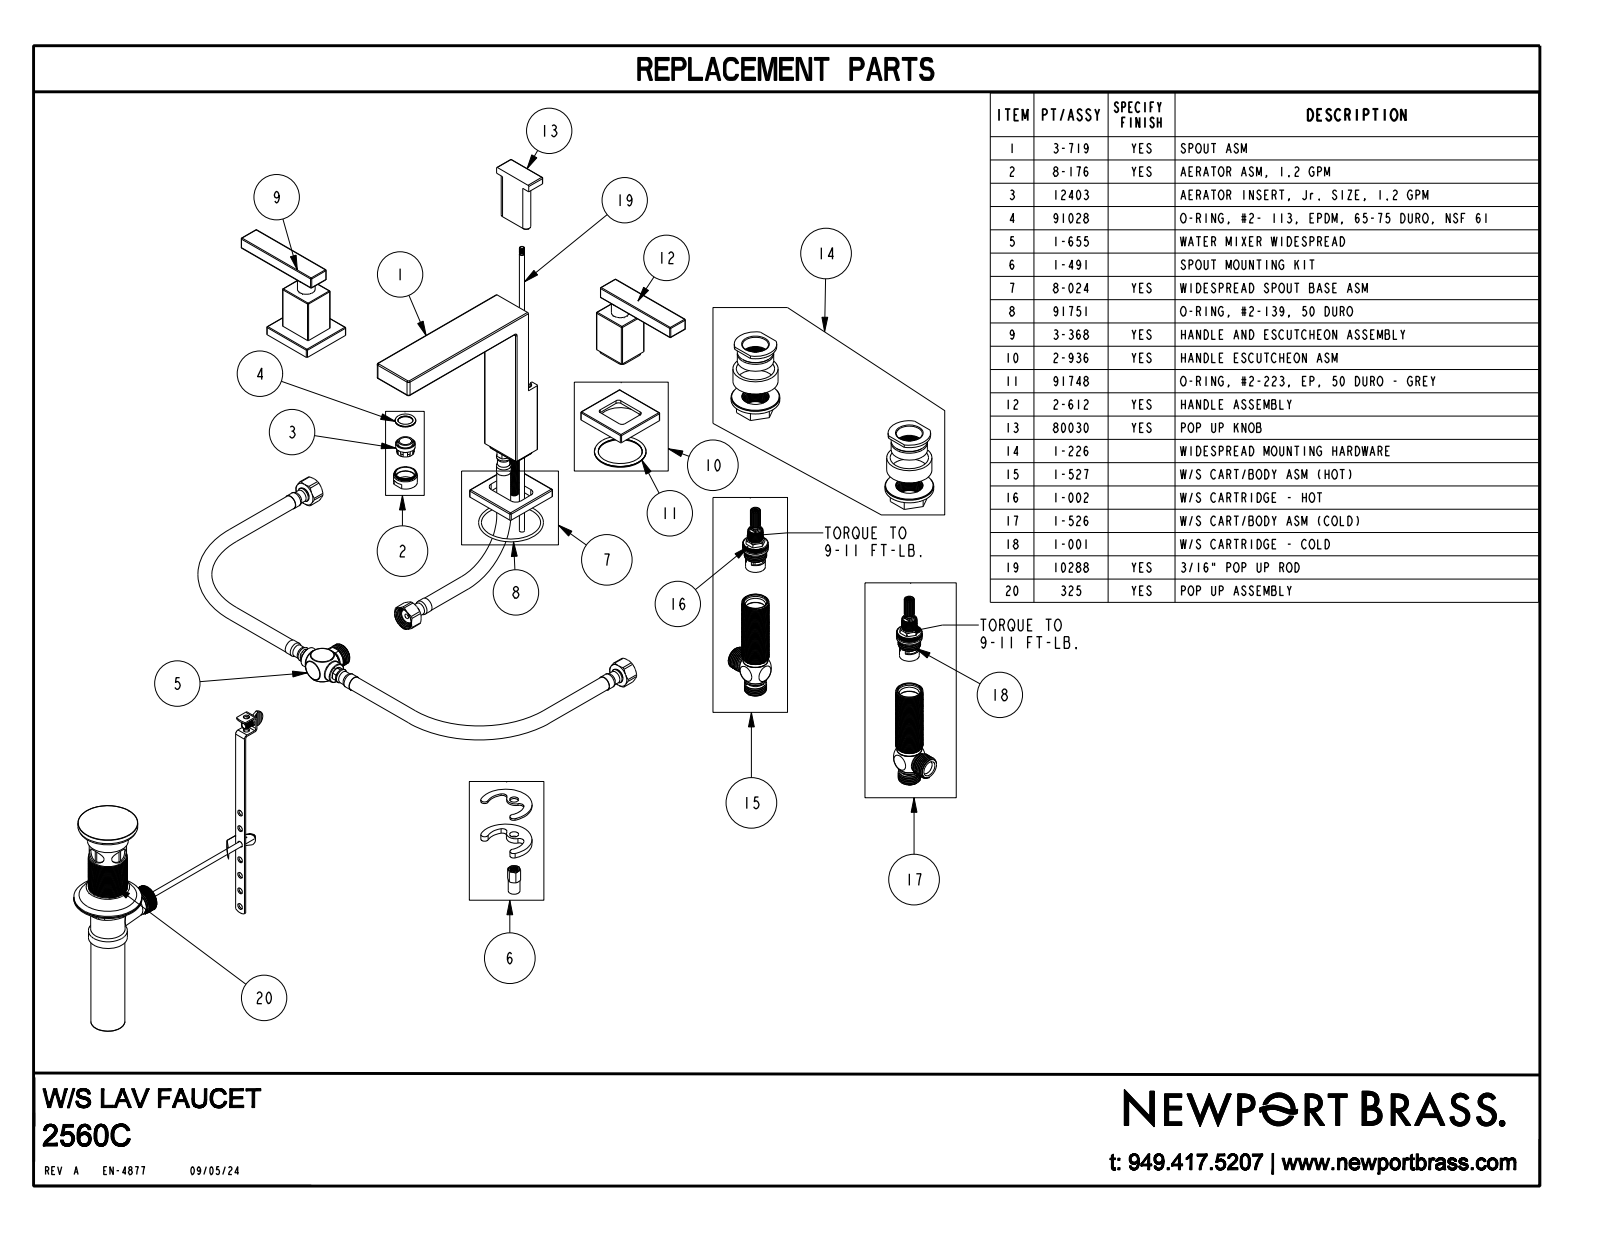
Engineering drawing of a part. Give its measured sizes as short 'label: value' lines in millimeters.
name: 2560C
written by: CREO PARAMETRIC BY PTC INC, 2019352 (CONFIG_CONTROL_DESIGN)
unit: mm
bodies: 5 solids, 1748 faces (588 planar, 783 cylindrical, 377 other)
size: 355.6 × 184.6 × 171.3
volume: 203 400 mm³; area: 225 000 mm²
holes: 3× ⌀16.5, 2× ⌀2.7, 2× ⌀3.6, 2× ⌀8.9, 2× ⌀9.5, 2× ⌀10.9, 2× ⌀11.5, 2× ⌀12.9, 2× ⌀13, 2× ⌀13.3, 2× ⌀14.3, 2× ⌀14.5
bosses: 2× ⌀48.2, 2× ⌀41.7, 2× ⌀10.2, 2× ⌀10.1, 2× ⌀9.7, 2× ⌀7.6, 2× ⌀7.1, 2× ⌀6.7
rounds: 48× R0.8, 40× R1, 12× R0.3, 12× R1.1, 8× R0.5, 8× R3.2, 8× R3.8, 8× R6.4
face distances: 2.8, 42.4, 0.5, 29, 16.6, 13.2, 13.8, 16, 144.4, 161
hole spacings: 172.5, 11.7, 13.7, 17, 93.9, 98.1, 98.2, 105.5
